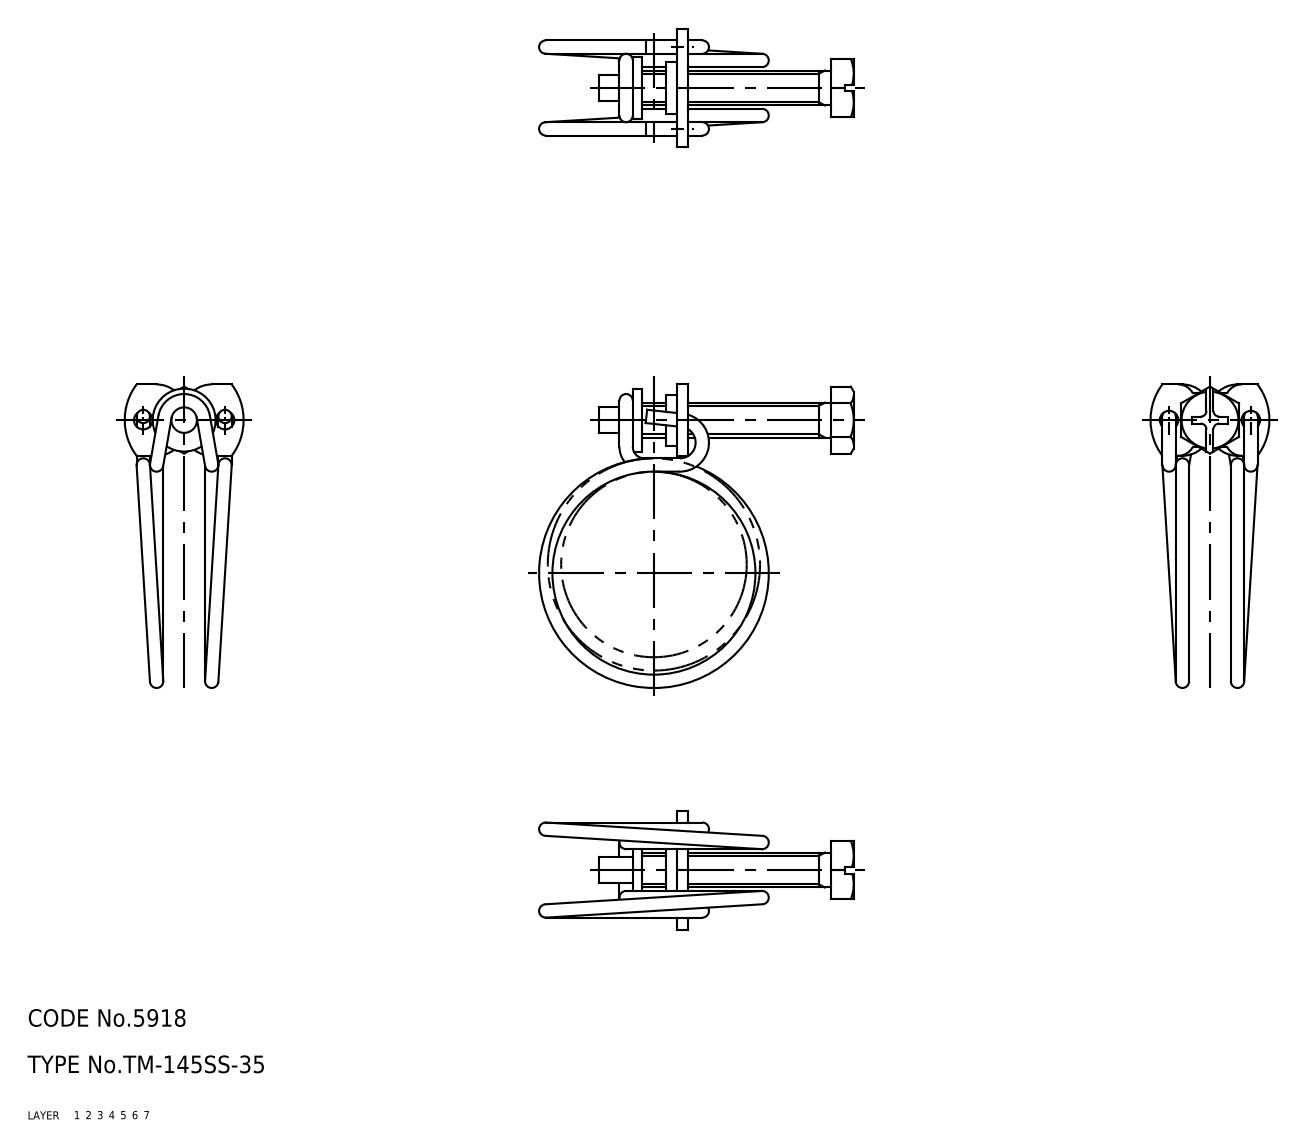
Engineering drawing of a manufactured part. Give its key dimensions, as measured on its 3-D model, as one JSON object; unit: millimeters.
{"part_name": "67116460; 67116473; 67116486", "step_written_by": "CADfix (AUTOMOTIVE_DESIGN)", "units": "millimeters", "bodies": {"solids": 3, "faces": 98, "planar": 0, "cylindrical": 0, "other": 98}, "overall_size": [54.25, 52.34, 20.5], "volume_mm3": 3190, "surface_area_mm2": 4139}
